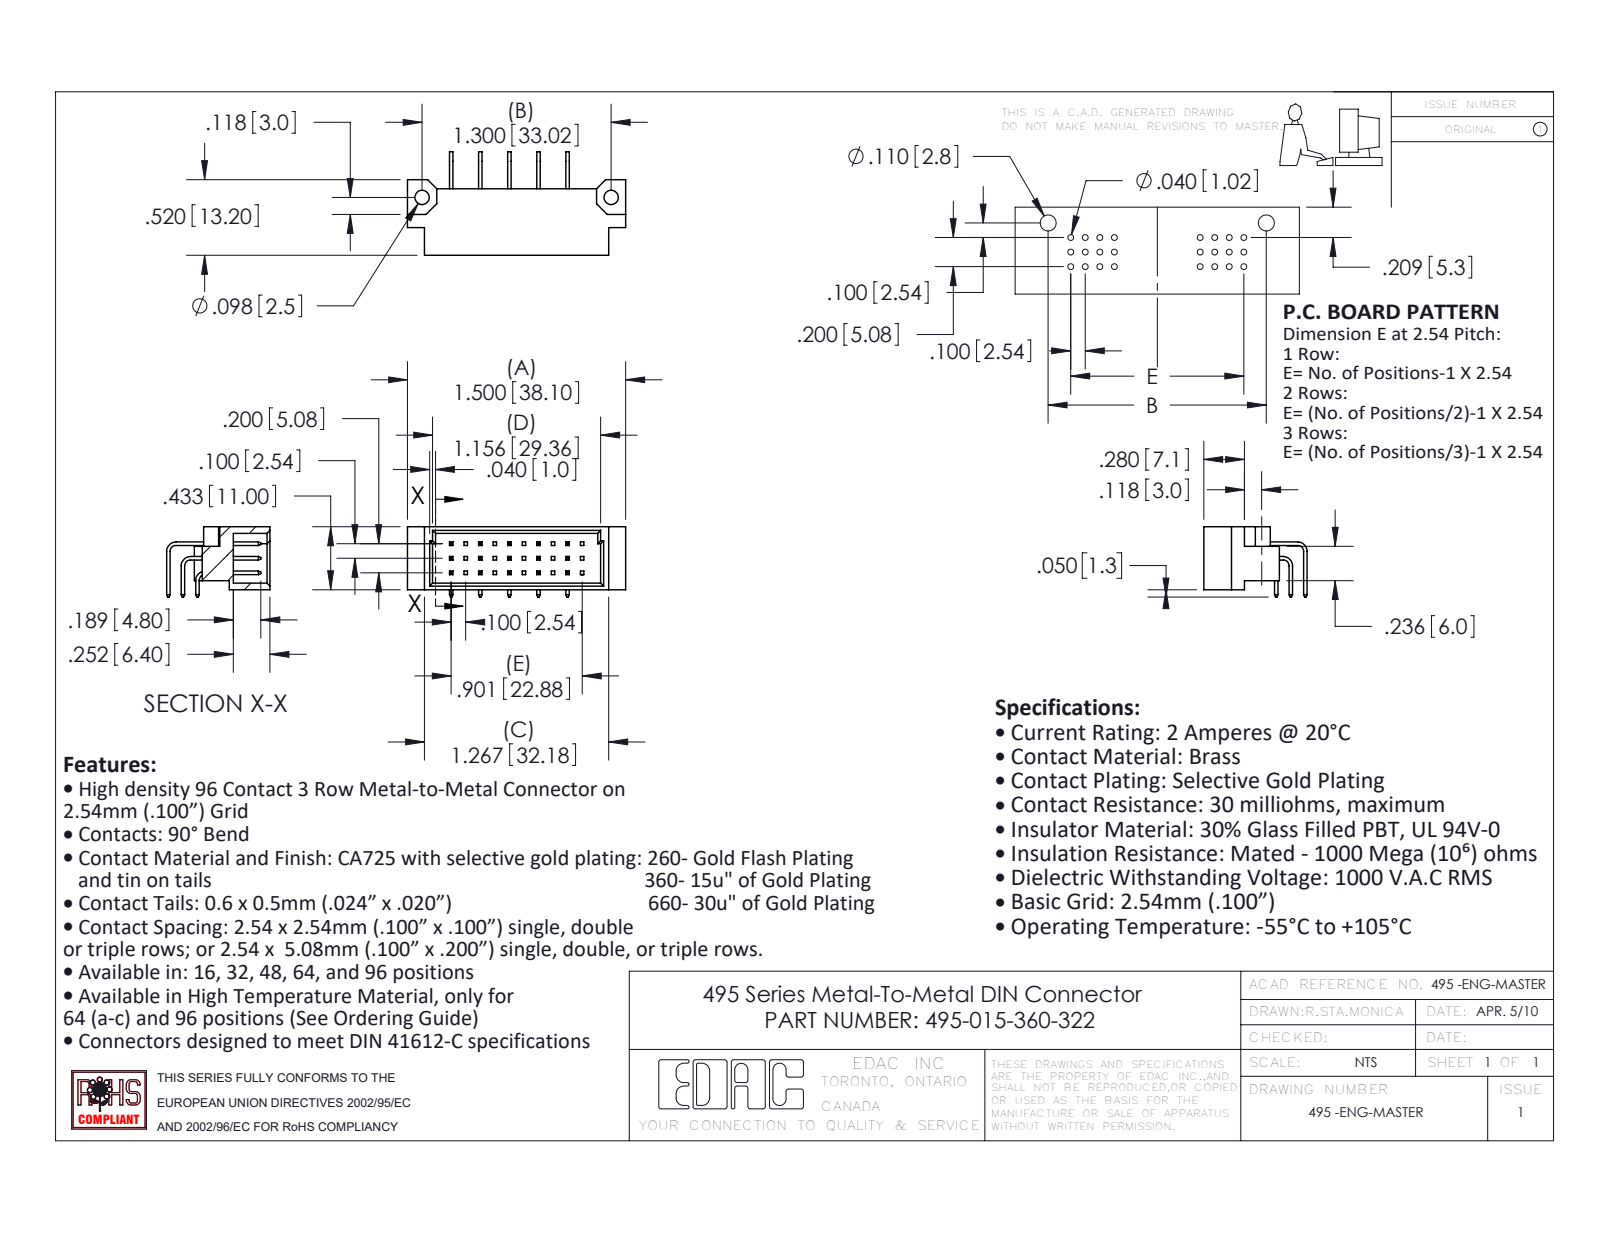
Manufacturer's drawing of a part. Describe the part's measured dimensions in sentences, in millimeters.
The part is named "495-015-360-322; 495-290-3; 495 Part_30; 495-290-1 (+1 more)". Its 3-D file was written by "SolidWorks 2020 (AUTOMOTIVE_DESIGN)". It is 16 solids with 439 faces: 405 planar, 34 cylindrical and 0 other. Overall it measures 38.1 by 18.05 by 12.27 millimeters. Its volume is 2 568 cubic millimeters and its surface area 3 569 square millimeters. Round holes: 2 of diameter 2.49. Partial cylindrical surfaces (rounded edges, fillets, slot ends): 3 of radius 1.02, 3 of radius 1.65. The main face-to-face distances are 5.08, 9.86, 1.14, 2.54, 5.2, 10.16, 0.61, 11, 0.6, 1.6. The hole center spacings are 33.02.
